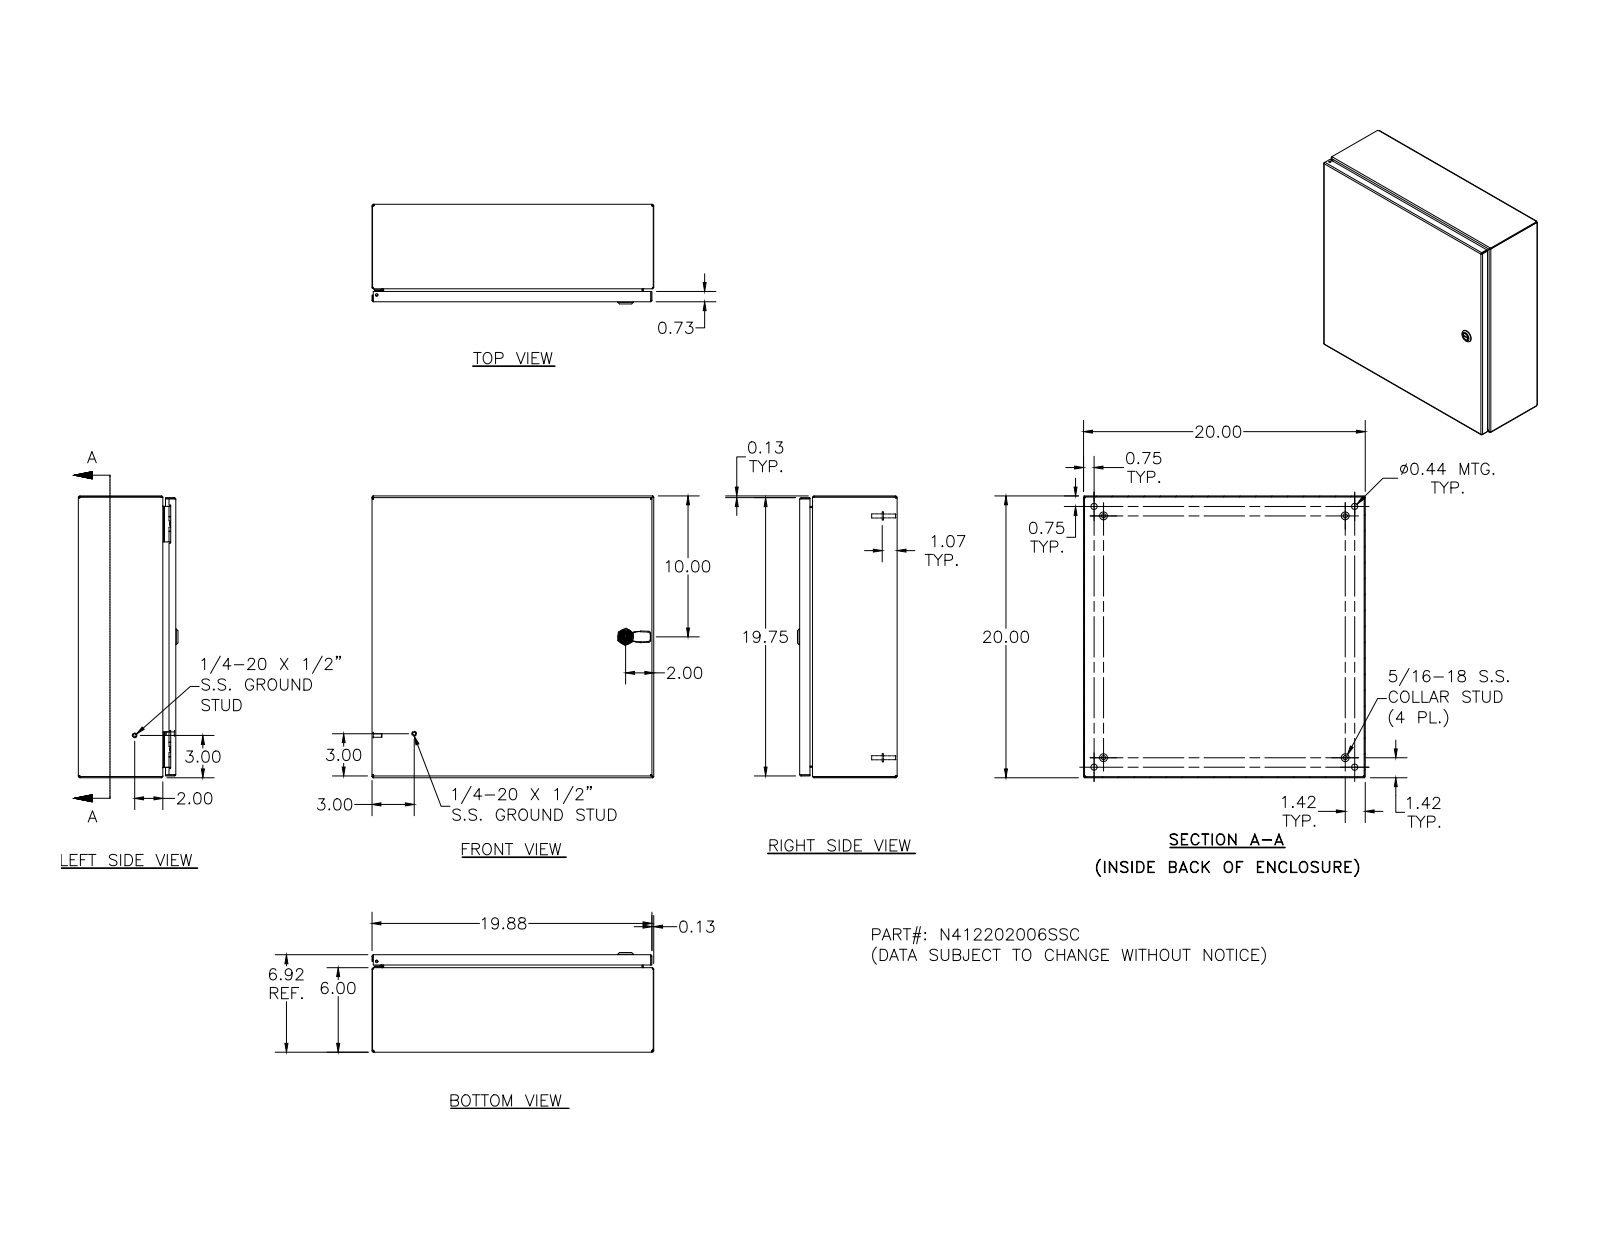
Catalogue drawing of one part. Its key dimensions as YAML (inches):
part_name: "N412202006SSC; N412202006SSCBKP; 388151; N4122020SSCLID (+8 more)"
step_written_by: "Autodesk Inventor 2011 (AUTOMOTIVE_DESIGN)"
units: inches
bodies: {solids: 34, faces: 1384, planar: 531, cylindrical: 509, other: 344}
overall_size: [20, 20, 7.075]
volume: 106.9
surface_area: 2906
round_holes:
  - {diameter: 0.188, count: 5}
  - {diameter: 0.093, count: 4}
  - {diameter: 0.152, count: 4}
  - {diameter: 0.167, count: 4}
  - {diameter: 0.172, count: 4}
  - {diameter: 0.437, count: 4}
  - {diameter: 0.156, count: 2}
  - {diameter: 0.187, count: 1}
  - {diameter: 0.197, count: 1}
  - {diameter: 0.315, count: 1}
  - {diameter: 0.394, count: 1}
  - {diameter: 0.402, count: 1}
round_bosses_or_shafts:
  - {diameter: 0.25, count: 10}
  - {diameter: 0.563, count: 4}
  - {diameter: 0.36, count: 4}
  - {diameter: 0.32, count: 4}
  - {diameter: 0.3, count: 4}
  - {diameter: 0.275, count: 4}
  - {diameter: 0.256, count: 4}
  - {diameter: 0.164, count: 4}
partial_cylinders:
  - {radius: 0.031, count: 30}
  - {radius: 0.05, count: 26}
  - {radius: 0.105, count: 20}
  - {radius: 0.016, count: 18}
  - {radius: 0.125, count: 14}
  - {radius: 0.02, count: 9}
  - {radius: 0.032, count: 8}
  - {radius: 0.07, count: 8}
face_to_face_distances: [0.074, 6.843, 19.926, 6.769, 6.917, 19.852, 20, 5.926, 0.917, 0.739]
hole_center_spacings: [16, 0.017, 0.66, 16.008, 18.5, 18.872, 0.019, 0.5]
